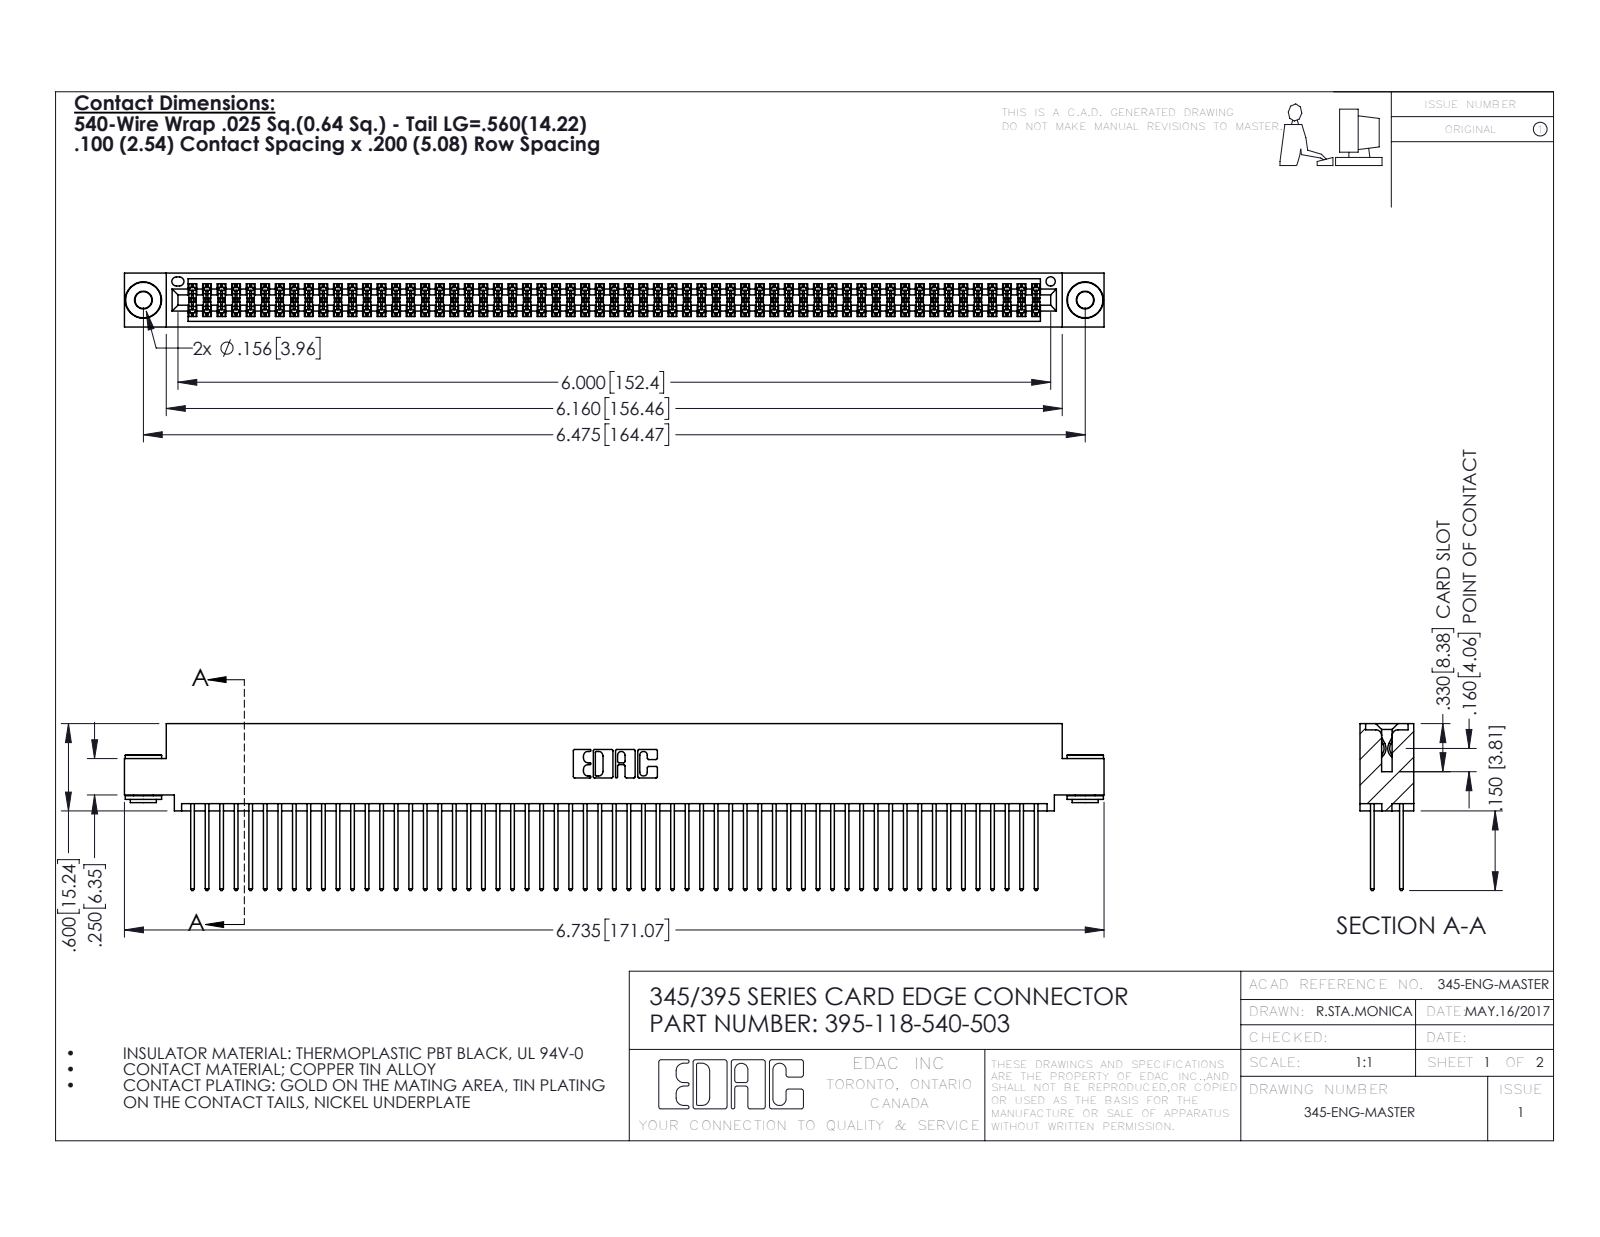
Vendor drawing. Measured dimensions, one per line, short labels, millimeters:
name: 345-292-001_345-293-140; 345-250-002_345-250-002-102; 345 Part_0.110 Offset - 0.156 Dia-TH; 395-118-540-503
written by: SolidWorks 2016 (CONFIG_CONTROL_DESIGN)
unit: mm
bodies: 121 solids, 6068 faces (3988 planar, 2072 cylindrical, 8 other)
size: 171.1 × 29.1 × 9.4
volume: 17 170 mm³; area: 28 080 mm²
holes: 2× ⌀2.9, 2× ⌀4, 1× ⌀1.6
bosses: 2× ⌀6.4, 2× ⌀4.6, 2× ⌀3.5
rounds: 177× R0.2, 118× R0.3, 22× R0.3, 6× R0.2, 6× R0.8, 3× R0.7, 2× R0.4, 2× R0.5
face distances: 1.8, 7.6, 5.1, 0.6, 2.5, 6.9, 9.4, 5.7, 4.4, 3.8
hole spacings: 6.9, 158.5, 164.5
